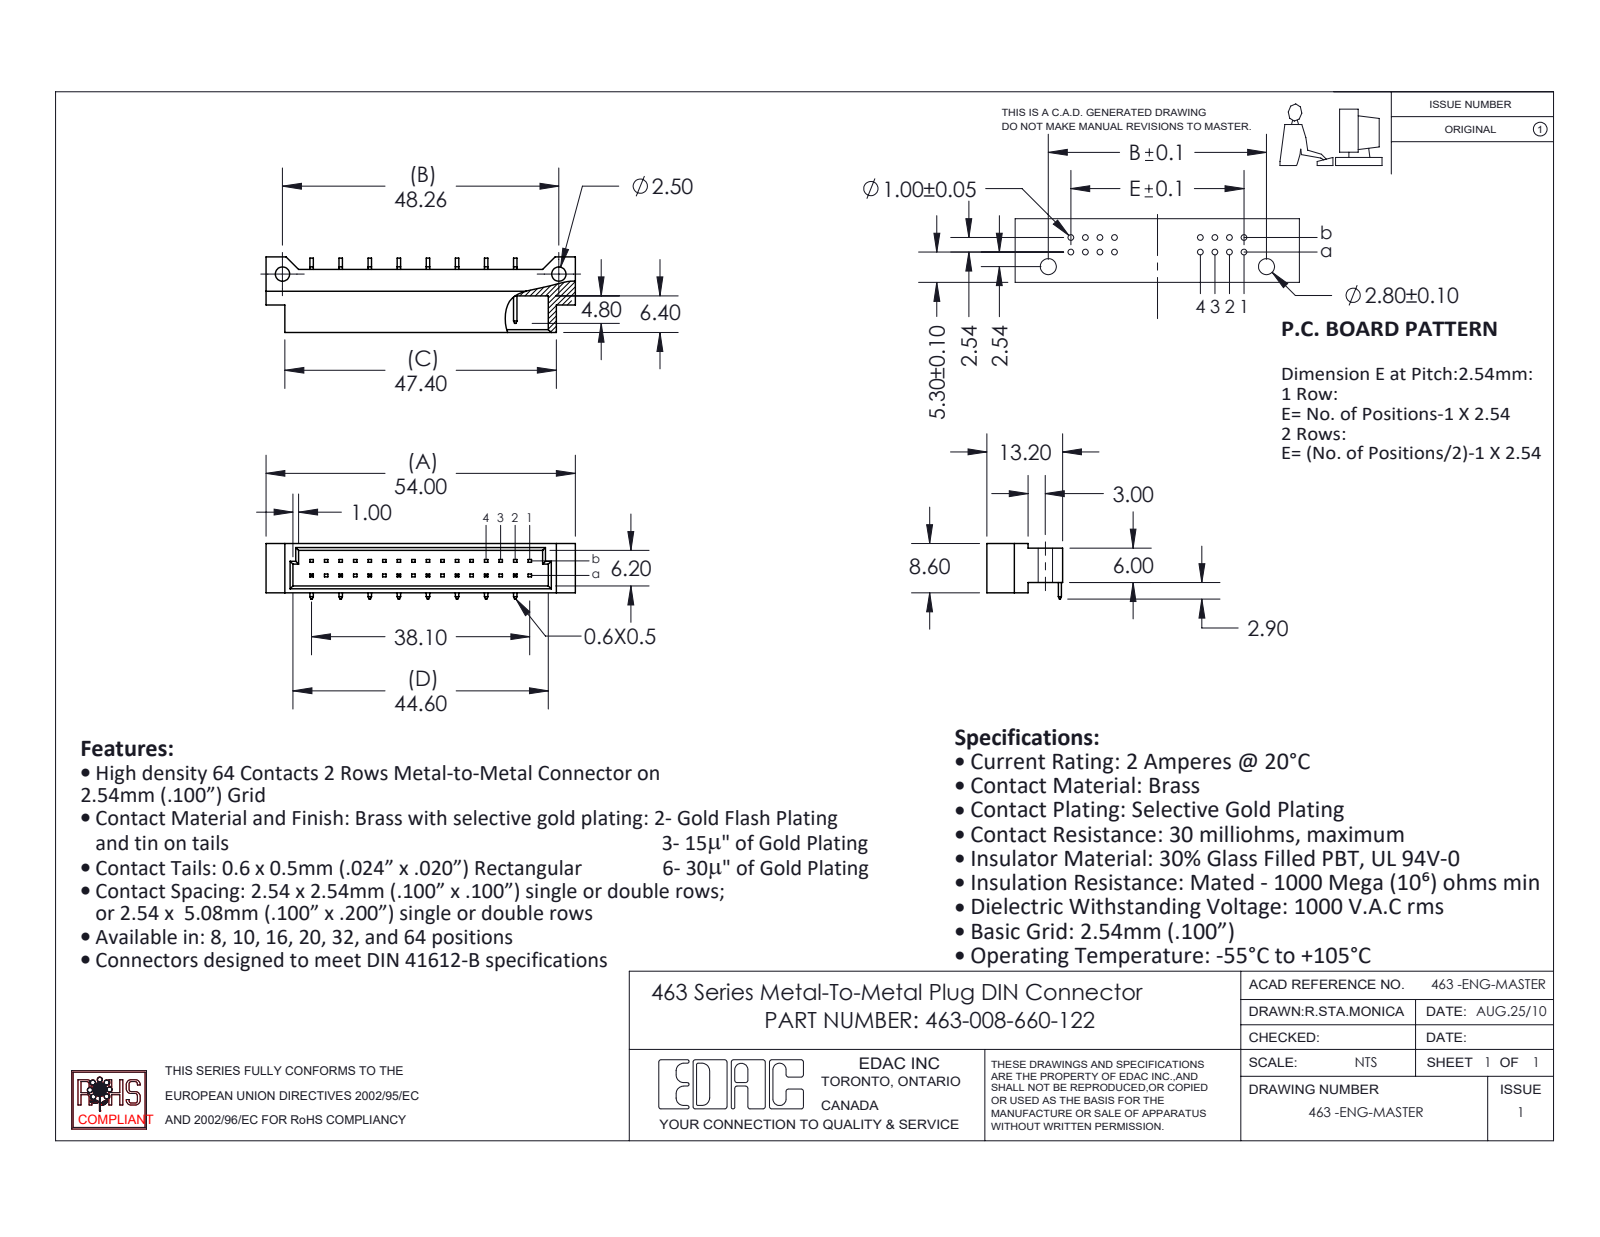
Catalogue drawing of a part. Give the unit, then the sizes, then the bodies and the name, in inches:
Units: inches
Overall size (bounding box): 2.126 × 0.52 × 0.382
Round holes (diameter × count): ⌀0.098 ×2
Partial cylindrical surfaces — rounded edges, fillets, slot ends (radius × count): R0.04 ×1, R0.06 ×1
Main face-to-face distances: 0.047, 0.291, 0.339, 0.031, 0.244, 0.024, 0.236, 0.268, 0.181, 0.22
Hole centre spacings: 1.9
Volume: 0.159 in³ · Surface area: 5.513 in²
Bodies: 9 solids, 311 faces (291 planar, 20 cylindrical, 0 other)
Part name (STEP PRODUCT): 463-008-660-122; 463 Part_32; 463-290-1
STEP written by: SolidWorks 2020 (CONFIG_CONTROL_DESIGN)
